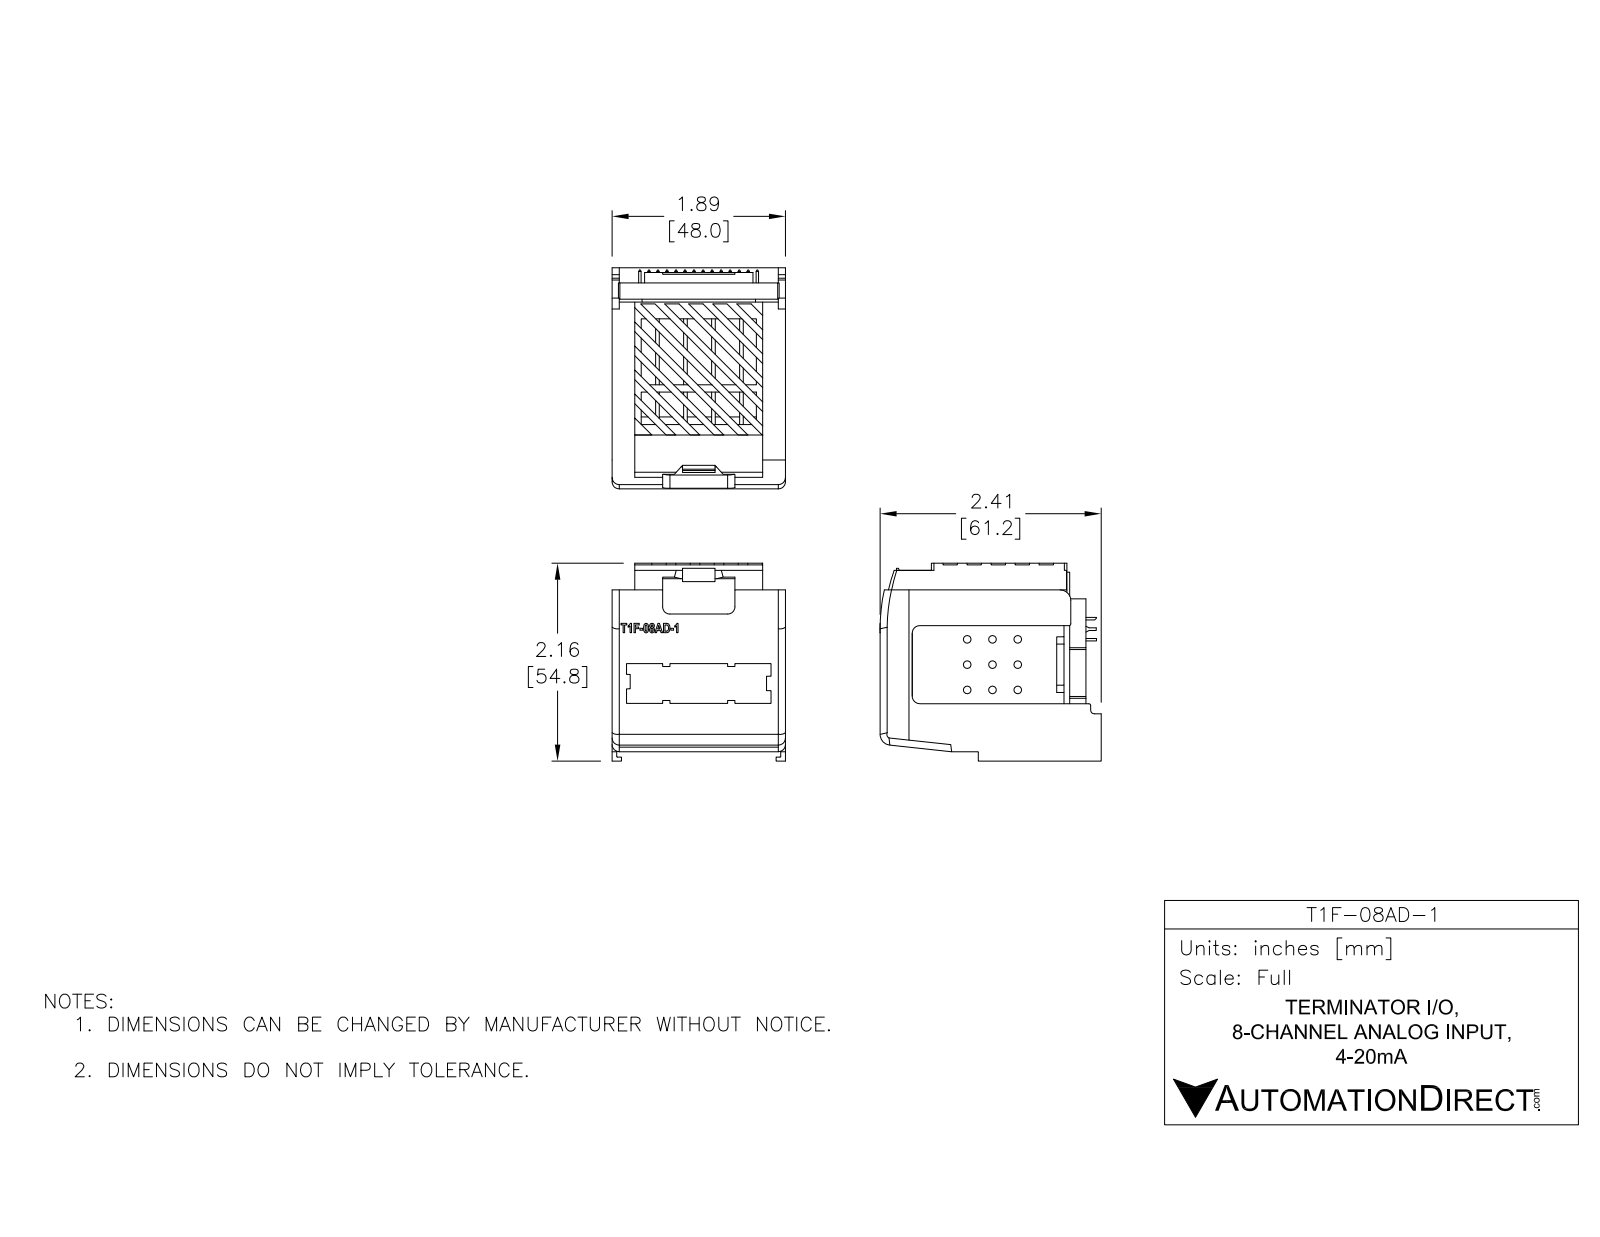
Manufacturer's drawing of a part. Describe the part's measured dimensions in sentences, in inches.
The part is named "T1F-08AD-1". Its 3-D file was written by "SolidWorks 2013 (AUTOMOTIVE_DESIGN)". It is 1 solid with 556 faces: 422 planar, 101 cylindrical and 33 other. Overall it measures 2.563 by 2.416 by 1.874 inches. Its volume is 1.848 cubic inches and its surface area 55.71 square inches. Round holes: 8 of diameter 0.118. Round bosses or shafts: 28 of diameter 0.028. Partial cylindrical surfaces (rounded edges, fillets, slot ends): 10 of radius 0.138, 5 of radius 0.039, 3 of radius 0.01, 3 of radius 0.022, 2 of radius 0.059, 1 of radius 0.315, 1 of radius 0.394, 1 of radius 0.709. The main face-to-face distances are 0.079, 1.795, 1.874, 1.717, 2.179, 1.965, 0.258, 1.537, 2.354, 0.39. The hole center spacings are 0.205, 0.409, 0.614, 0.819, 1.024, 1.228, 1.433.
